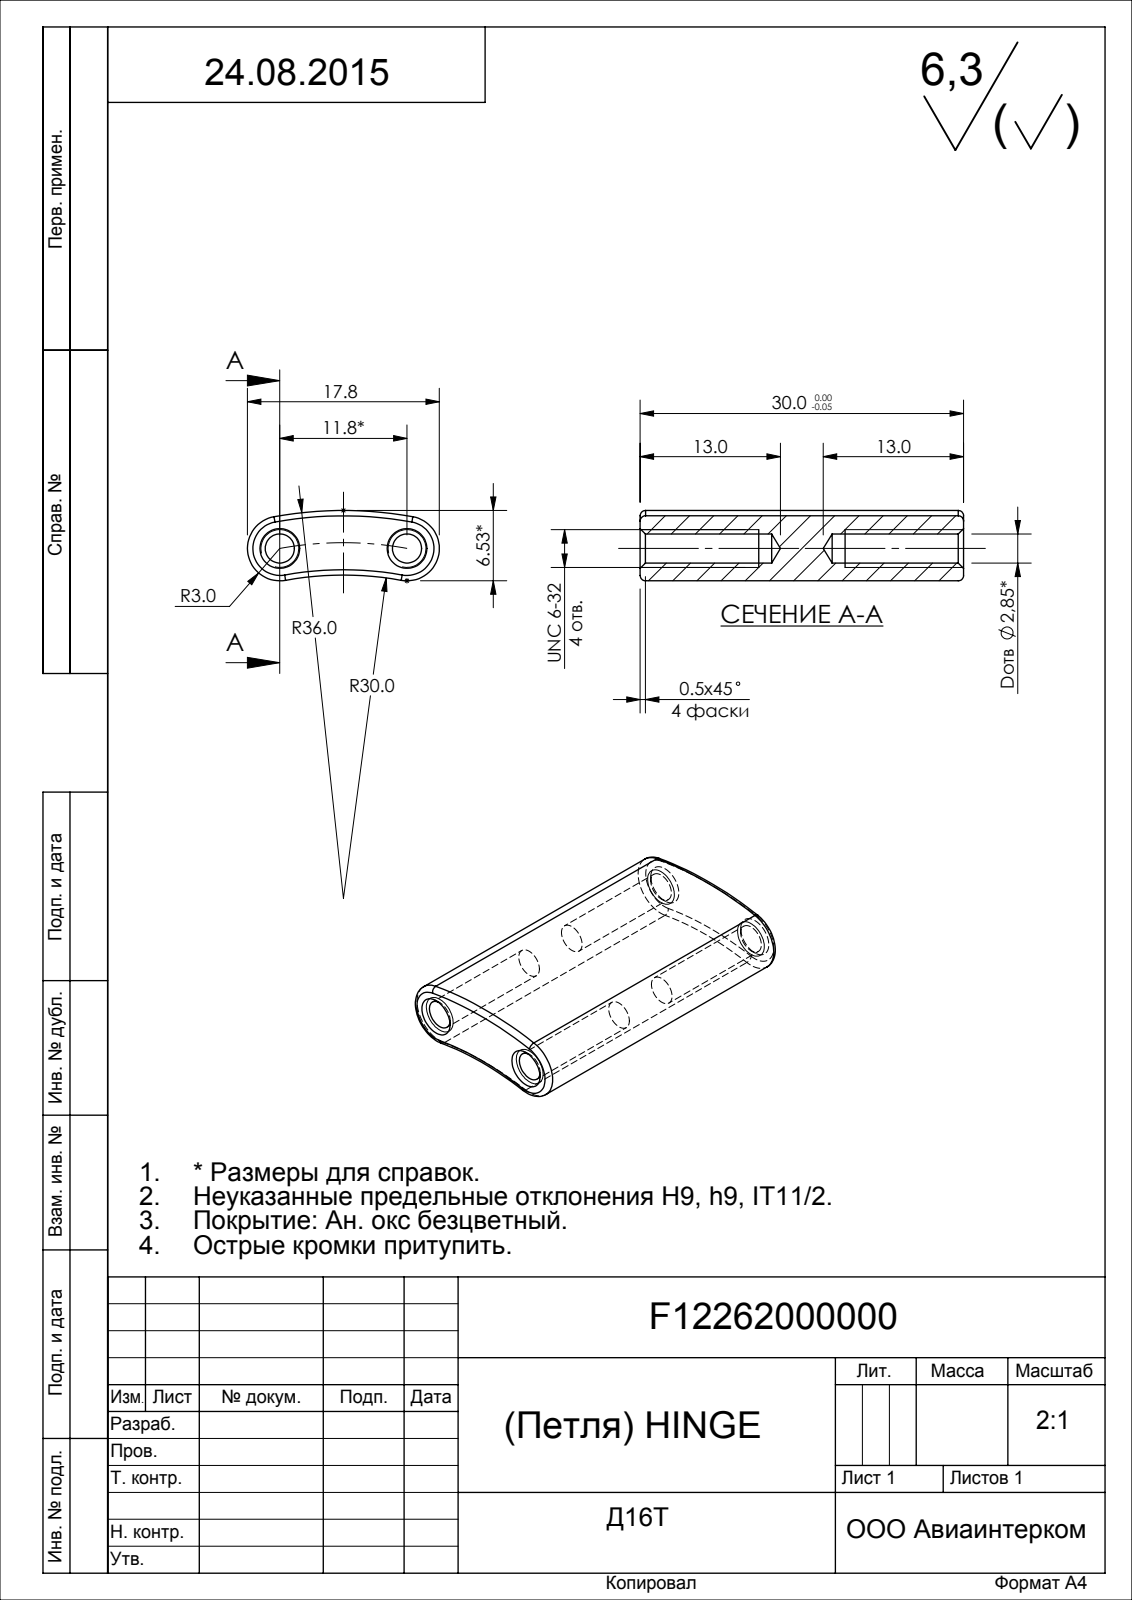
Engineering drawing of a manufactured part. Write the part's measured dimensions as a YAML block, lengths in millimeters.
part_name: "(Петля) HINGE F12262000000"
step_written_by: "SolidWorks 2017 (AUTOMOTIVE_DESIGN)"
units: millimeters
bodies: {solids: 1, faces: 33, planar: 2, cylindrical: 13, other: 18}
overall_size: [30, 17.8, 6.53]
volume: 2735
surface_area: 1844
round_holes:
  - {diameter: 2.5, count: 2}
partial_cylinders:
  - {radius: 3, count: 2}
  - {radius: 30, count: 1}
  - {radius: 36, count: 1}
face_to_face_distances: [30]
hole_center_spacings: [11.8]
